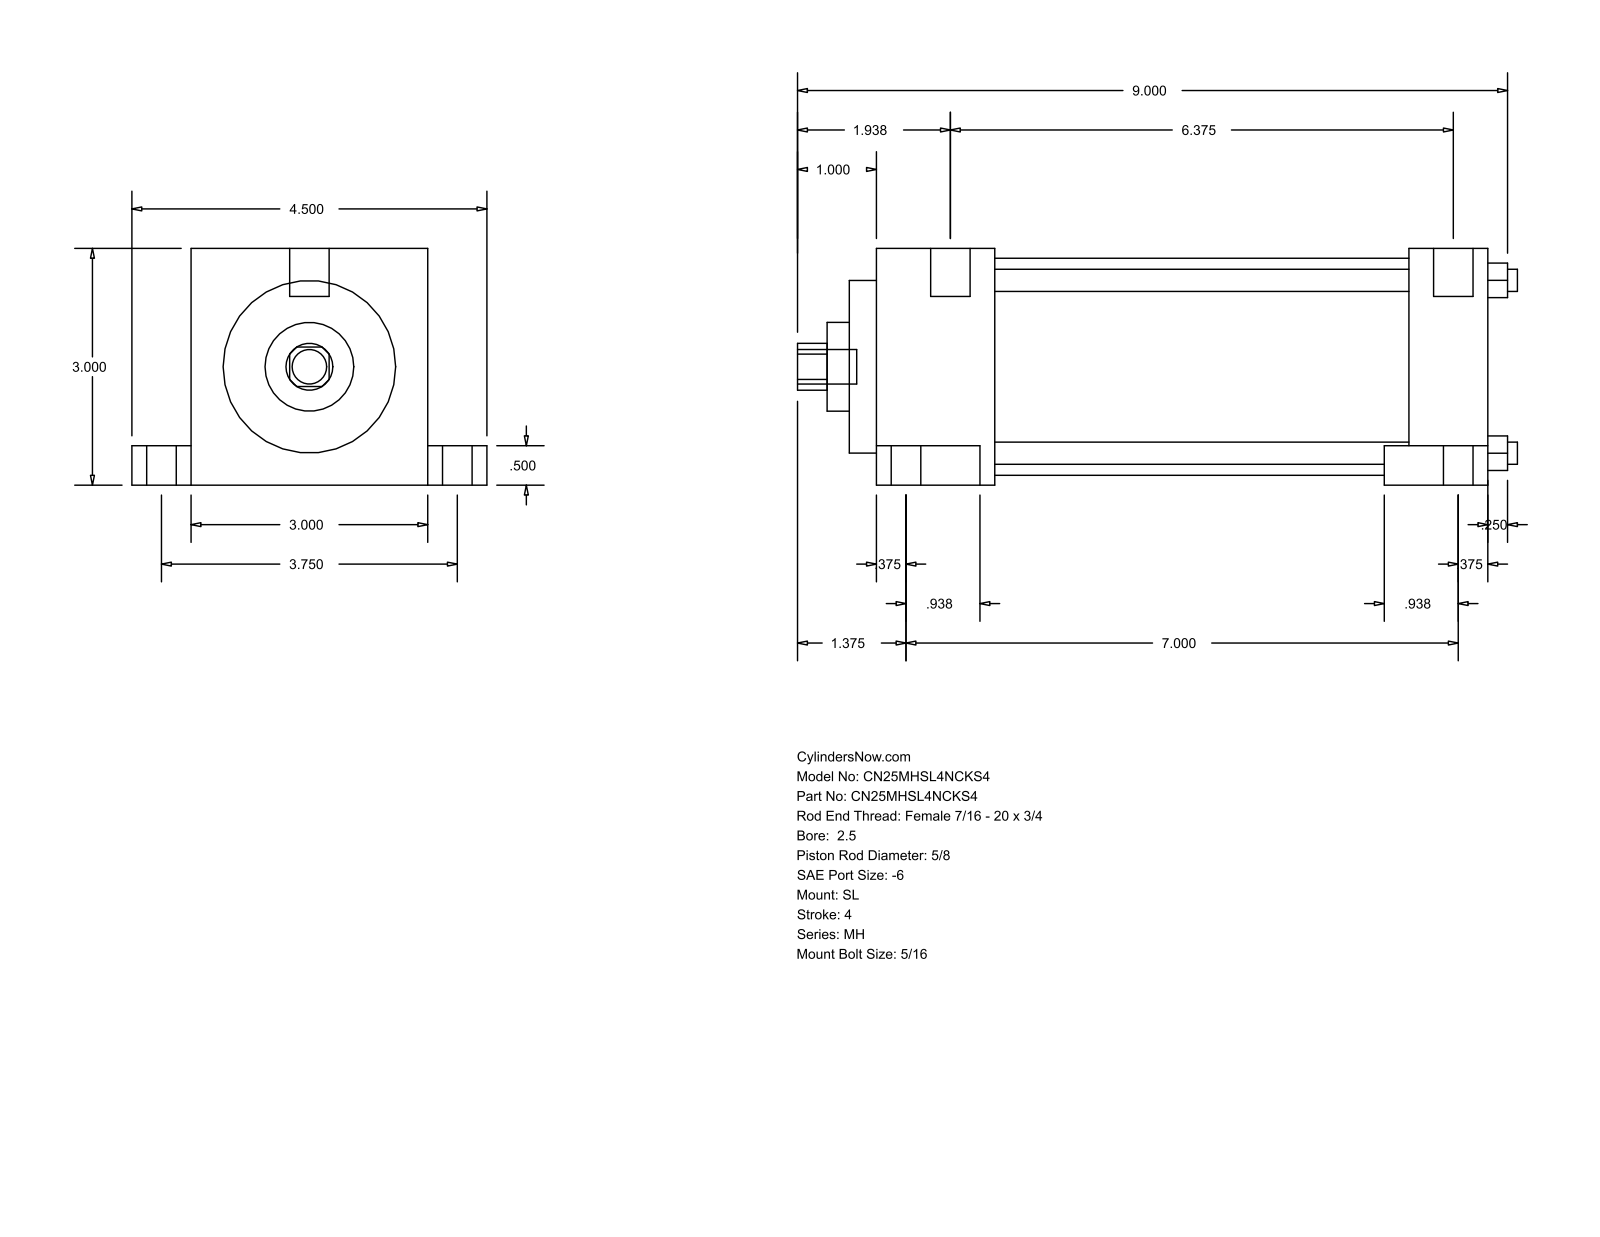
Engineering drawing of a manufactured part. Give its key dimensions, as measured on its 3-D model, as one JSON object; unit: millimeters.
{"part_name": "MH_SL__0250_0.625", "step_written_by": "GSSL Pune (CONFIG_CONTROL_DESIGN)", "units": "millimeters", "bodies": {"solids": 0, "faces": 86, "planar": 61, "cylindrical": 25, "other": 0}, "overall_size": [231.78, 114.3, 76.2], "round_holes": [[7.14, 4], [15.88, 1], [28.57, 1], [55.55, 1], [69.85, 1]], "round_bosses_or_shafts": [[15.88, 2], [9.53, 2], [5.56, 2], [12.7, 1], [11.11, 1]], "partial_cylinders_radius": [[7.54, 1]], "face_to_face_distances": [76.2, 25.4, 180.18, 205.58, 12.7, 63.5, 19.05, 95.25, 31.75, 172.24], "hole_center_spacings": [39.33, 55.62, 78.66]}
